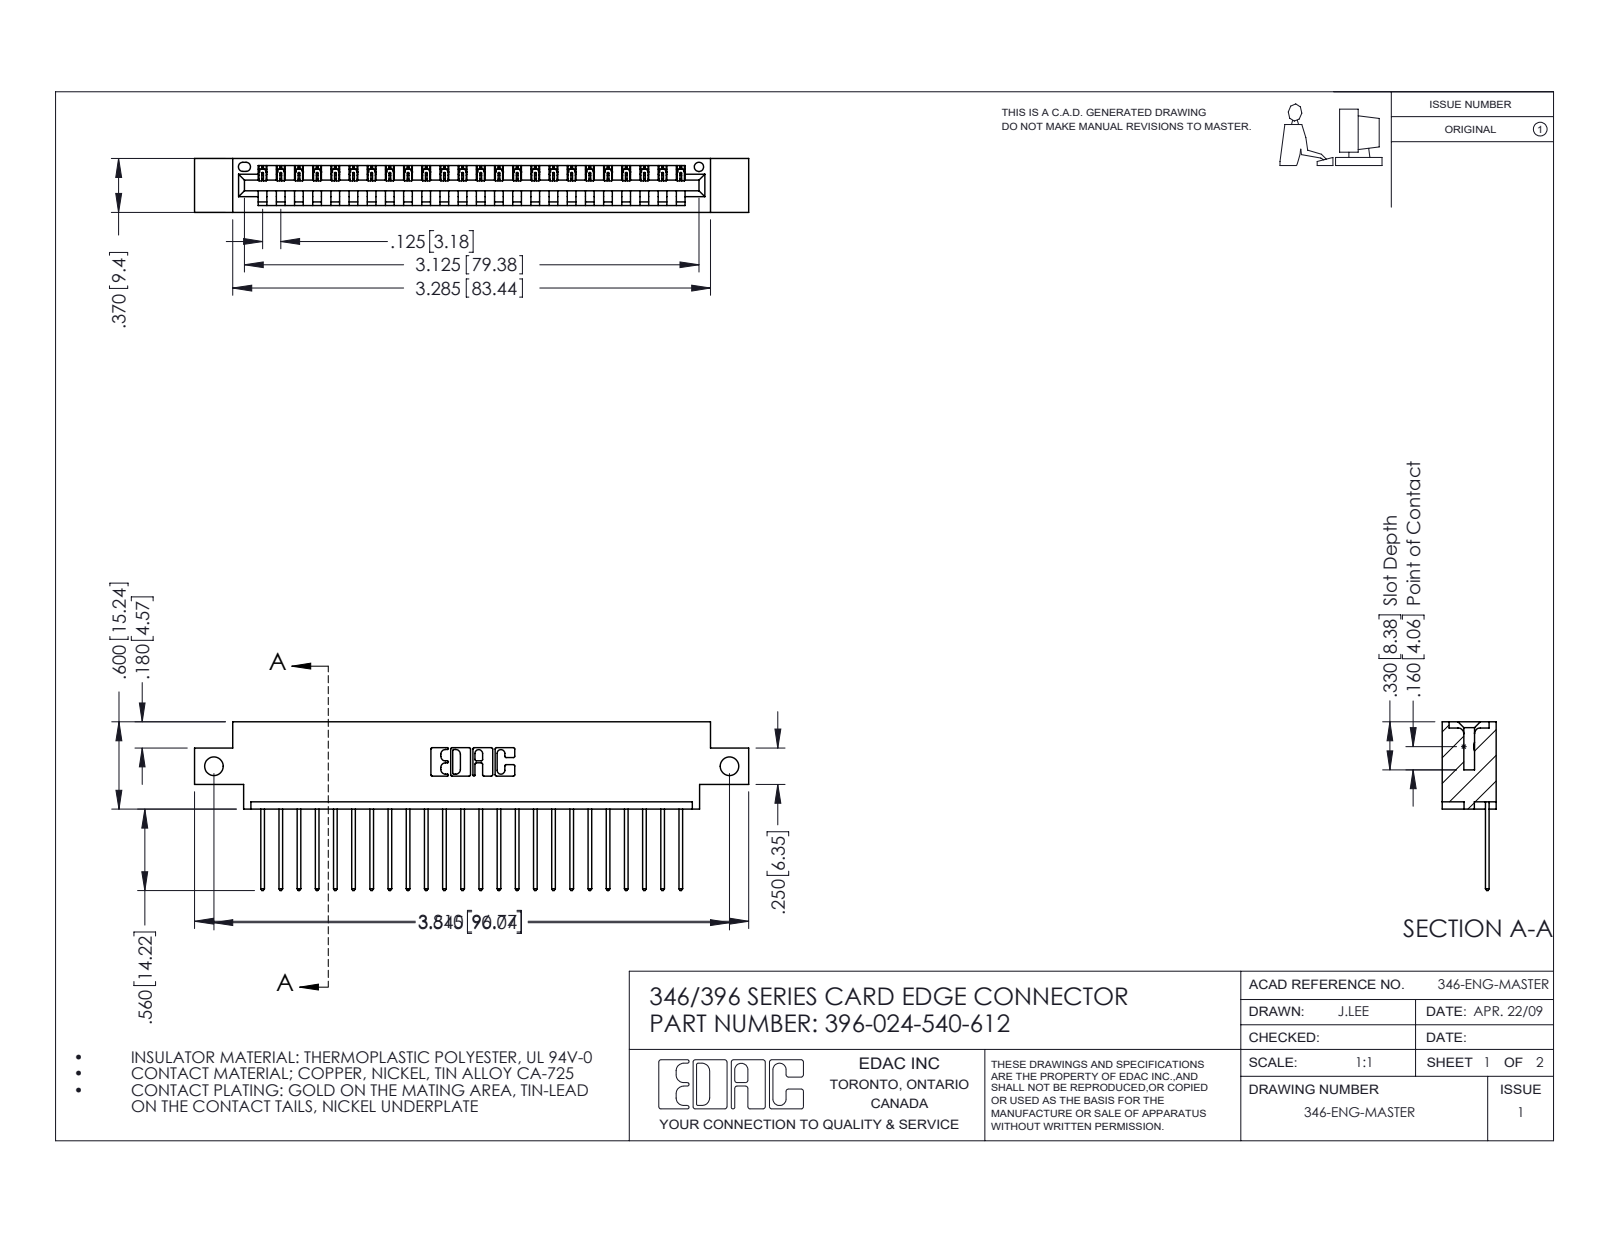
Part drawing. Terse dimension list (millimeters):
name: 396-024-540-612; 345-292-001_345-293-140; 346 Part_0.170 Offset - Side Mount
written by: SolidWorks 2016 (CONFIG_CONTROL_DESIGN)
unit: mm
bodies: 25 solids, 1518 faces (1040 planar, 478 cylindrical, 0 other)
size: 96.8 × 29.5 × 9.4
volume: 8 930 mm³; area: 11 220 mm²
holes: 2× ⌀3.3, 1× ⌀1.6
rounds: 48× R0.2, 48× R0.3, 22× R0.3, 6× R0.2, 6× R0.8, 3× R0.7, 2× R0.8, 2× R1
face distances: 1.2, 8.2, 9.4, 6.4, 1.8, 7.6, 0.6, 3.8, 5.6, 2.5
hole spacings: 90
